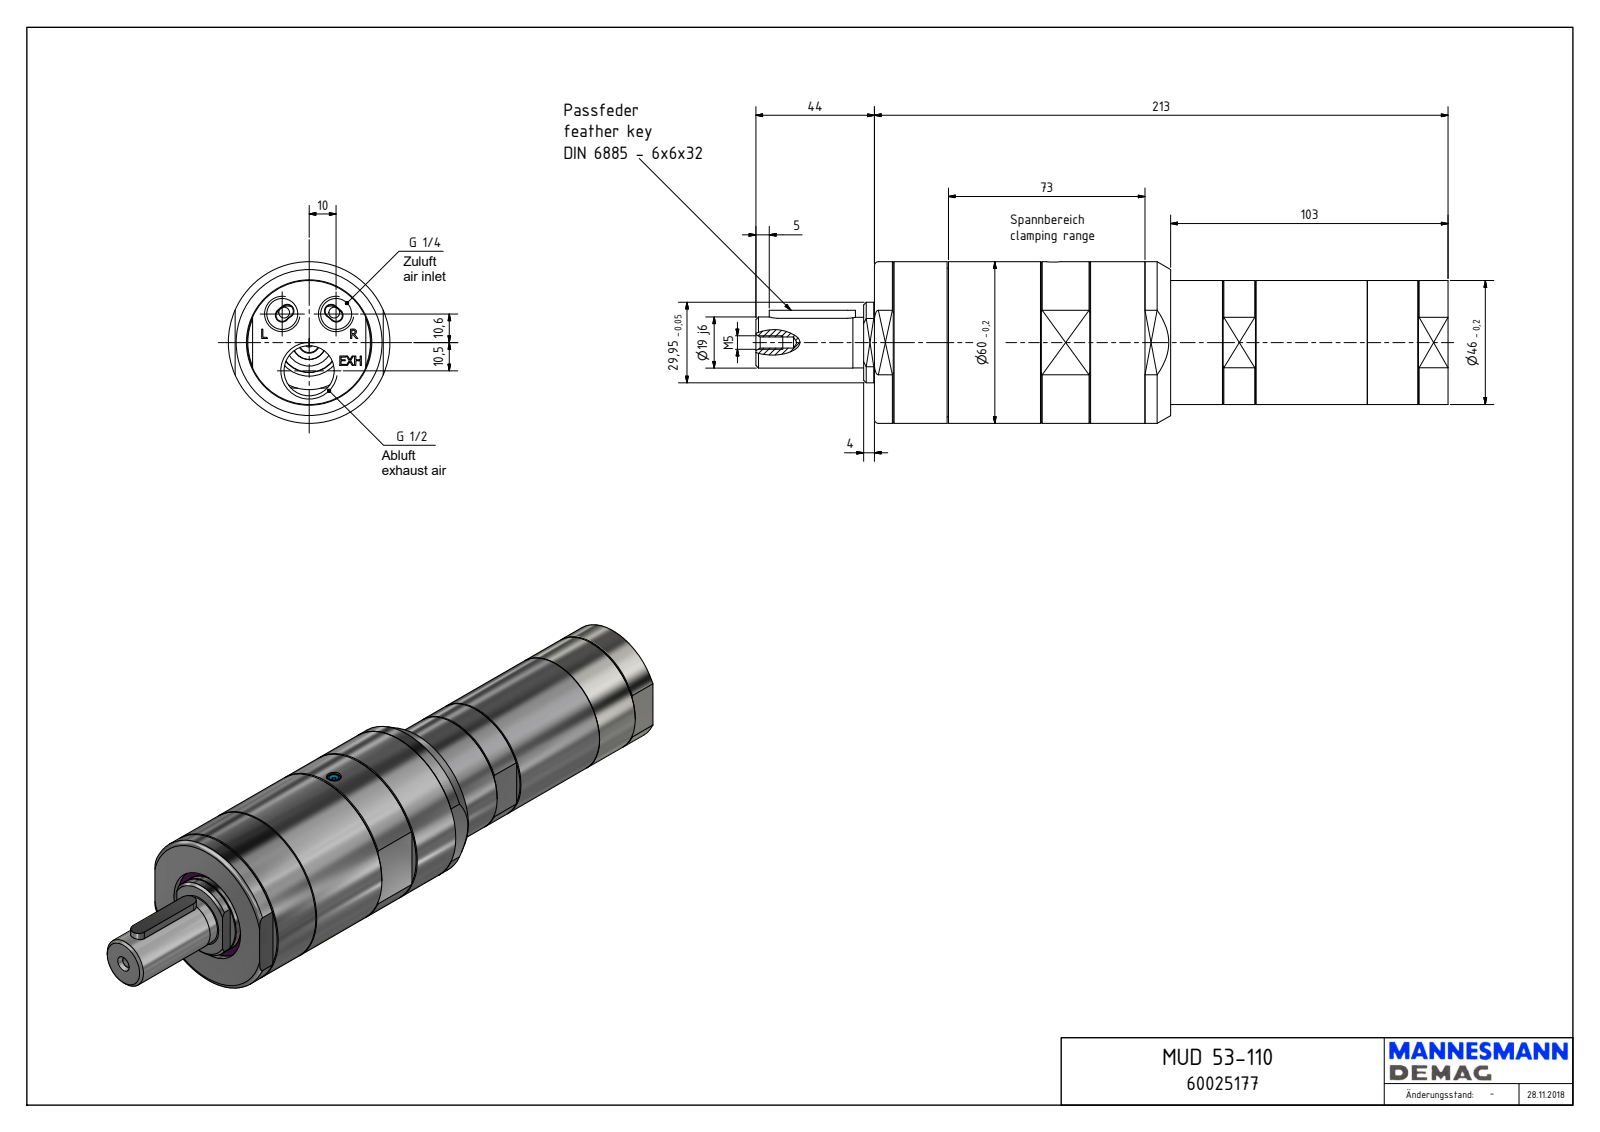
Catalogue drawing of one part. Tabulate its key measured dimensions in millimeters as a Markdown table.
| quantity | value |
| --- | --- |
| part name | MUD 53-110_60025177 |
| STEP written by | Autodesk Inventor 2018 (AUTOMOTIVE_DESIGN) |
| units | millimeters |
| bodies | 1 solid, 217 faces (117 planar, 47 cylindrical, 53 other) |
| overall size | 257 × 60 × 60 |
| volume | 485 237 mm³ |
| surface area | 51 320 mm² |
| round holes (diameter × count) | 11.45 × 2, 1.55 × 1, 4 × 1, 4.13 × 1, 5.5 × 1, 18.63 × 1, 35 × 1, 36.5 × 1, 40 × 1, 46.5 × 1, 55.38 × 1 |
| round bosses / shafts (diameter × count) | 60 × 1, 55.18 × 1, 46 × 1, 33.85 × 1, 29.95 × 1, 19 × 1, 18.8 × 1, 5 × 1 |
| partial cylindrical surfaces (radius × count) | 3 × 2, 5 × 2, 19 × 1, 26.78 × 1 |
| main face-to-face distances | 6.5, 213, 48.5, 55, 103, 110, 185.5, 27.5, 82.5, 24.5 |
| hole center spacings | 14.57, 23.35, 10.5, 20 |
